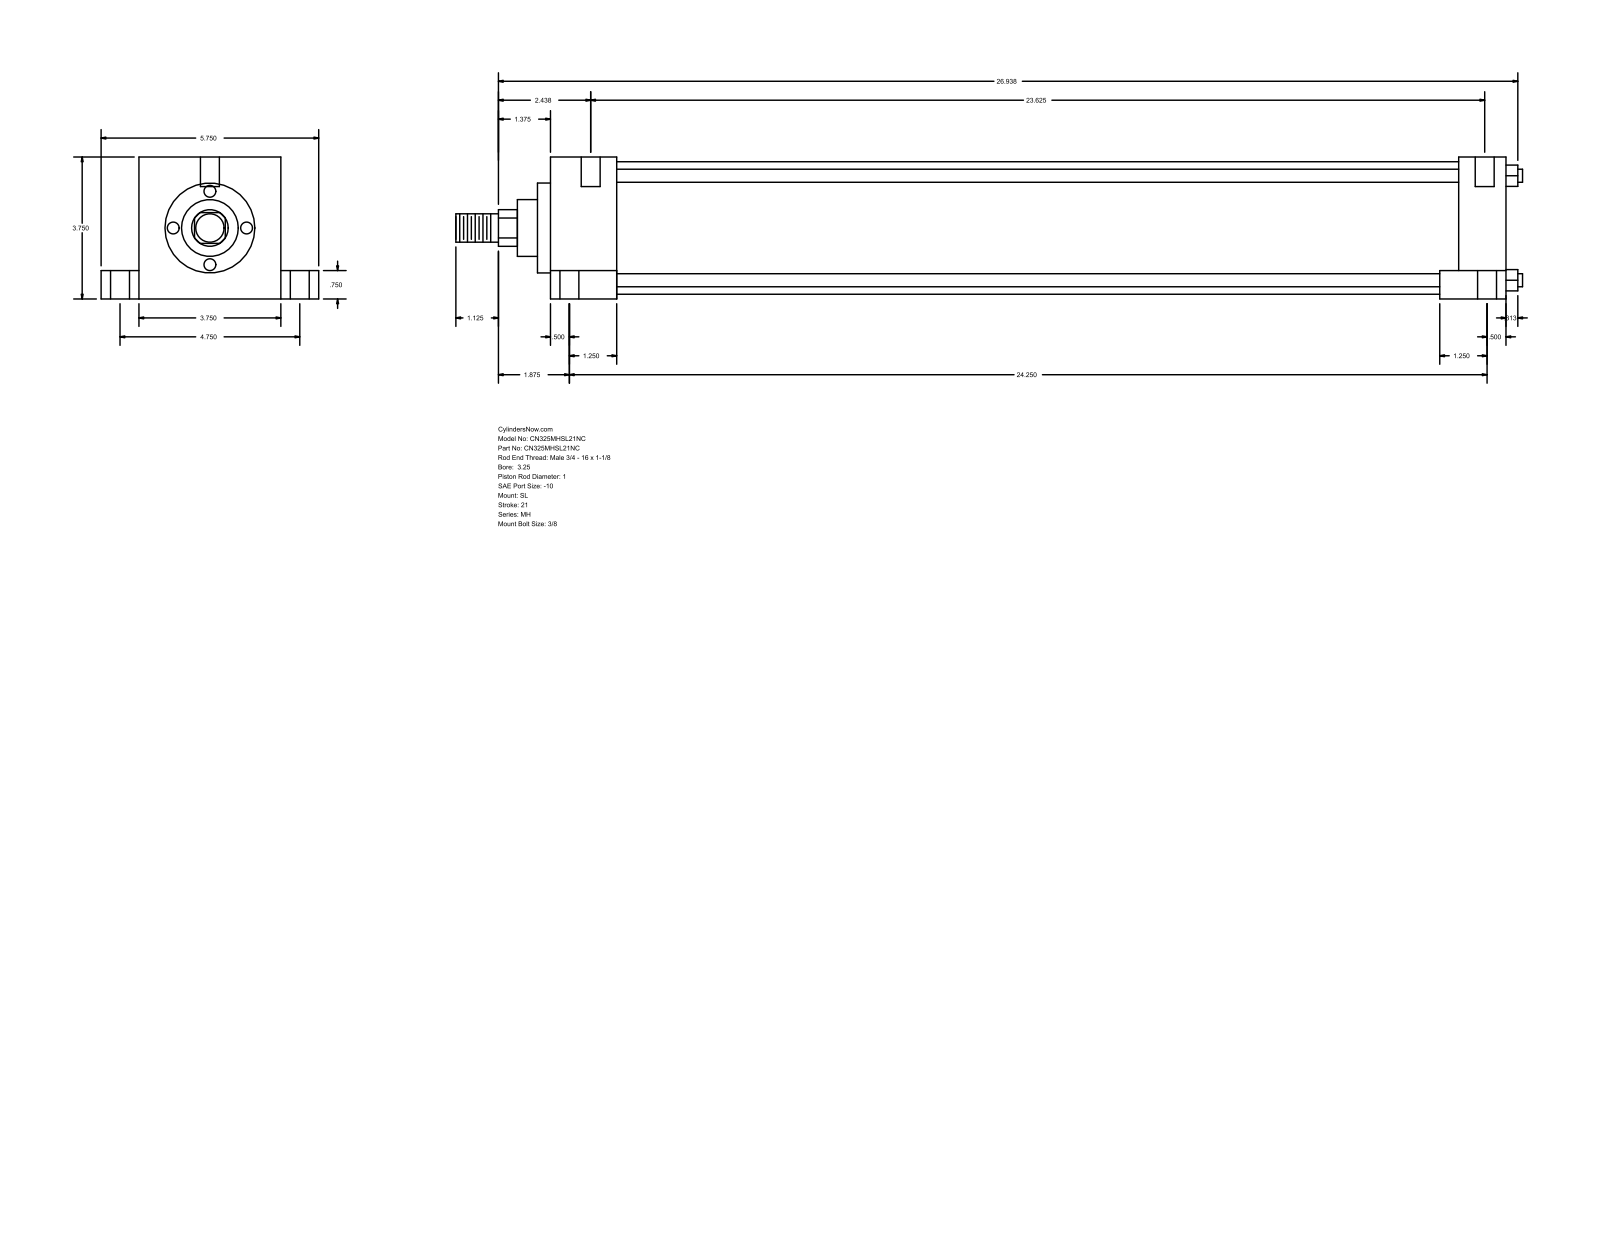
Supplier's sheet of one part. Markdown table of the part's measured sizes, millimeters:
| quantity | value |
| --- | --- |
| part name | MH_SL__0325_1 |
| STEP written by | GSSL Pune (CONFIG_CONTROL_DESIGN) |
| units | millimeters |
| bodies | 0 solids, 110 faces (77 planar, 33 cylindrical, 0 other) |
| overall size | 715.96 × 146.05 × 95.25 |
| round holes (diameter × count) | 12.7 × 6, 5.56 × 4, 19.05 × 4 |
| round bosses / shafts (diameter × count) | 8.76 × 4, 88.9 × 1, 60.33 × 1, 38.1 × 1, 25.4 × 1, 19.05 × 1 |
| partial cylindrical surfaces (radius × count) | 12.29 × 1 |
| main face-to-face distances | 95.24, 641.35, 44.46, 596.89, 25.41, 120.65, 19.05, 76.19, 609.6, 565.14 |
| hole center spacings | 60.35, 60.41, 61.65, 62, 120.66, 604.69, 606.26, 606.42 |
